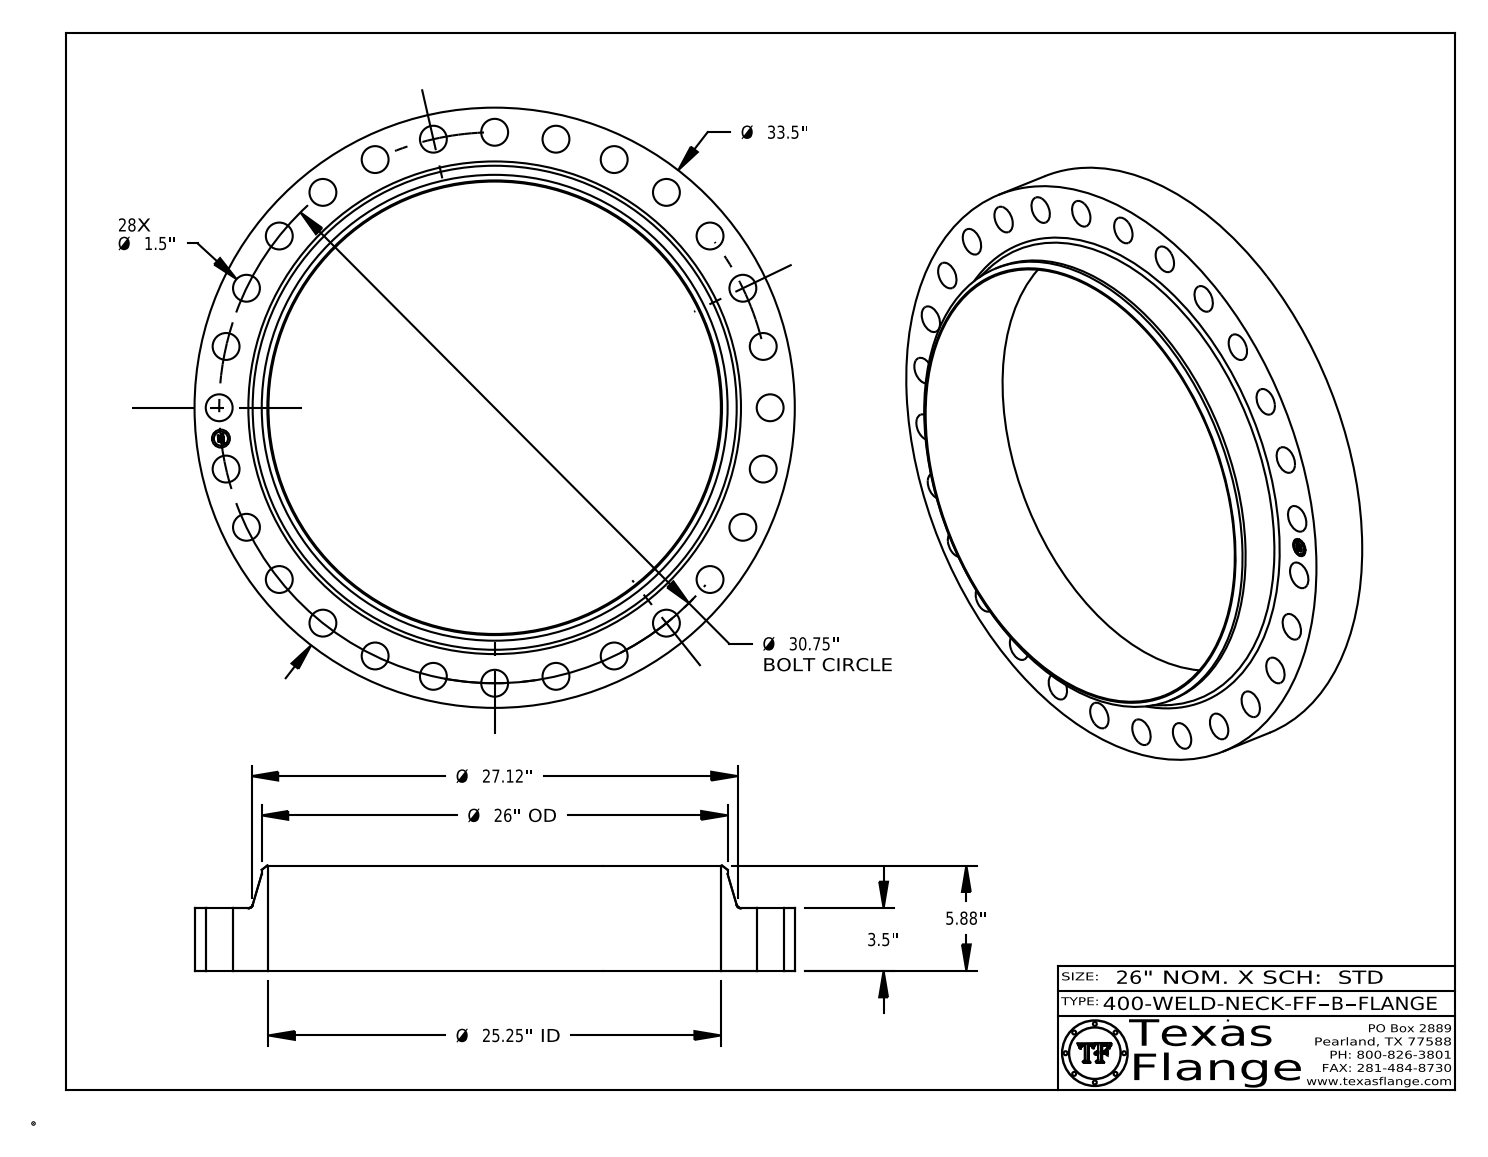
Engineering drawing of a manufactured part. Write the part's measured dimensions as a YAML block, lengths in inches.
part_name: "400-WELD-NECK-FF, Series B"
step_written_by: "CATIA V5 STEP AP214 (AUTOMOTIVE_DESIGN)"
units: inches
bodies: {solids: 1, faces: 456, planar: 368, cylindrical: 82, other: 6}
overall_size: [33.5, 33.5, 5.88]
volume: 1273
surface_area: 2099
round_holes:
  - {diameter: 1.5, count: 28}
  - {diameter: 1, count: 1}
  - {diameter: 25.25, count: 1}
round_bosses_or_shafts:
  - {diameter: 0.061, count: 8}
  - {diameter: 33.5, count: 1}
  - {diameter: 26, count: 1}
  - {diameter: 0.788, count: 1}
face_to_face_distances: [3.5, 5.88, 2.38, 3.485, 0.015, 2.395, 0.298, 0.293, 0.054, 0.193]
hole_center_spacings: [6.843, 29.024, 15.375, 21.743, 13.342, 16.36, 19.172, 26.037]
